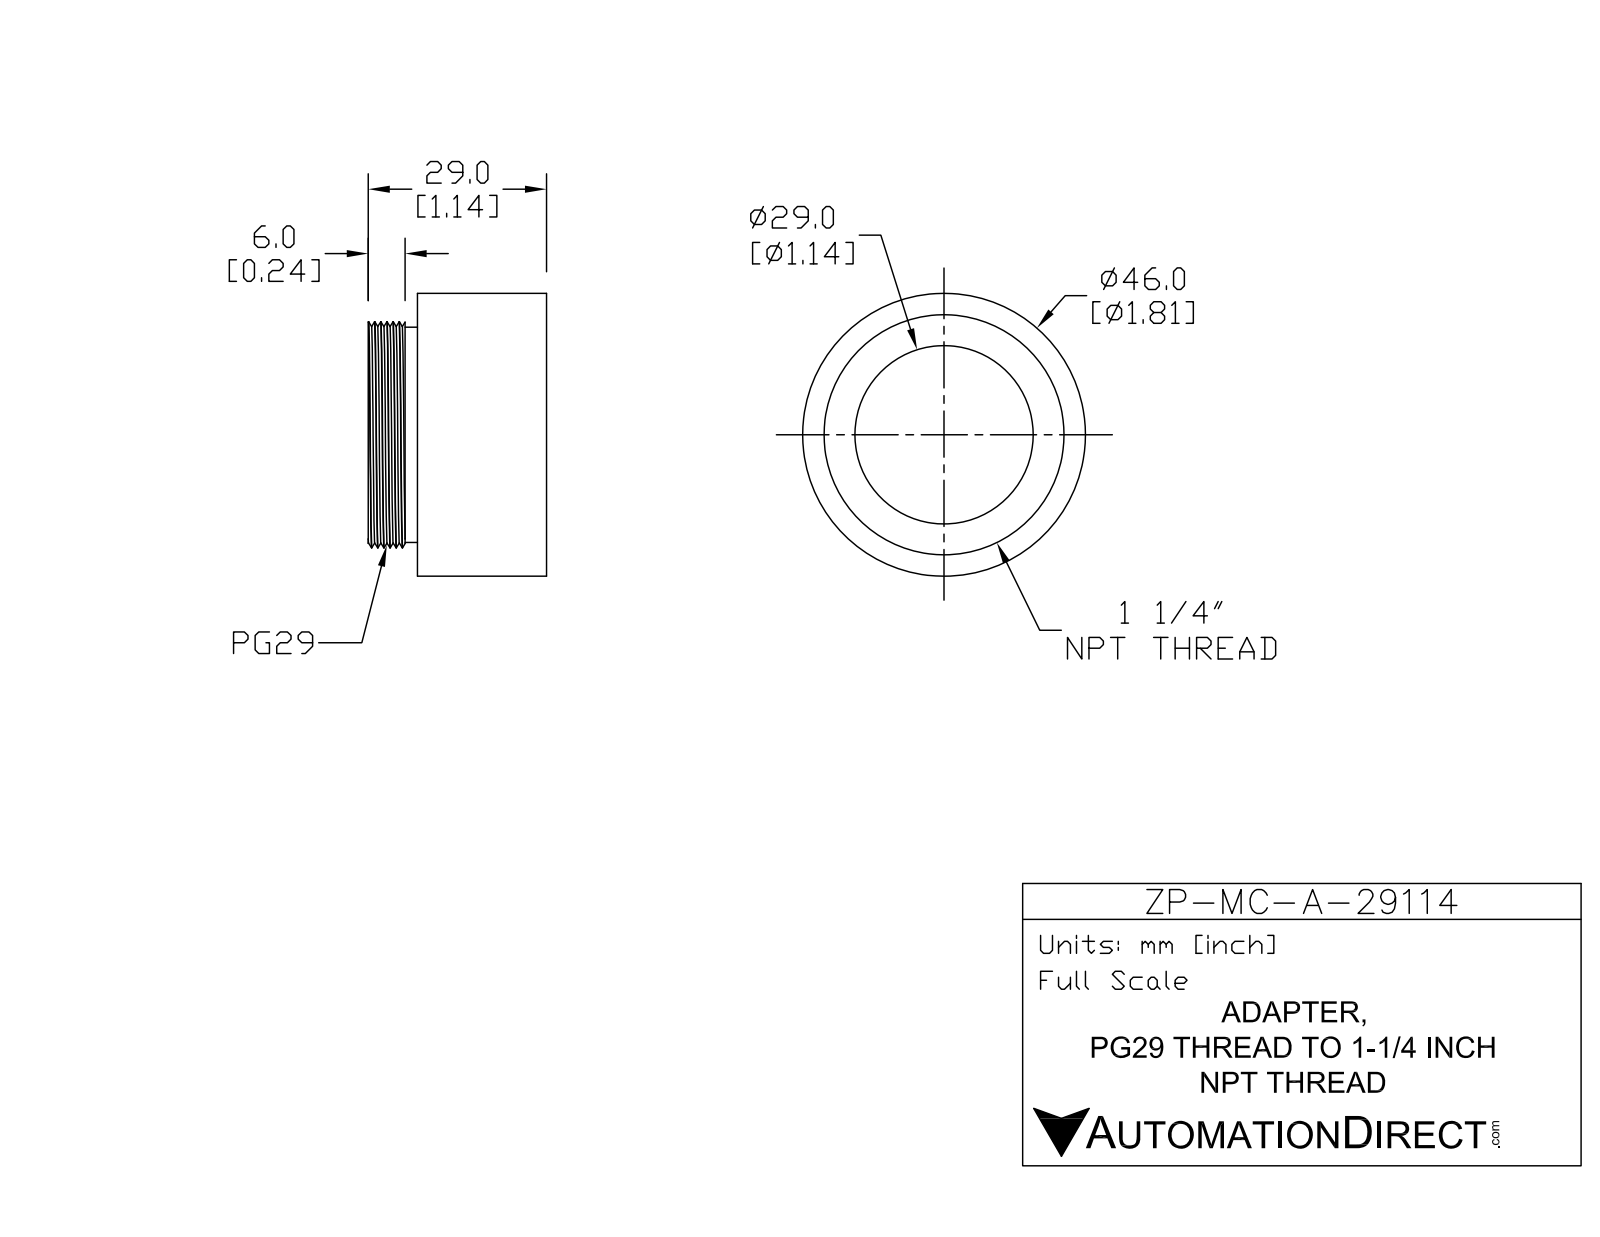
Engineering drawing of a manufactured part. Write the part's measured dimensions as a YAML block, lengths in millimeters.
part_name: "ZP-MC-A-29114"
step_written_by: "SolidWorks 2011 (AUTOMOTIVE_DESIGN)"
units: millimeters
bodies: {solids: 1, faces: 32, planar: 6, cylindrical: 22, other: 4}
overall_size: [46, 46, 29]
volume: 13267
surface_area: 12758
round_holes:
  - {diameter: 29, count: 1}
  - {diameter: 38.95, count: 1}
round_bosses_or_shafts:
  - {diameter: 46, count: 1}
  - {diameter: 36.75, count: 1}
  - {diameter: 35, count: 1}
face_to_face_distances: [3, 21, 18, 8, 11, 29, 6, 2, 5, 23]
